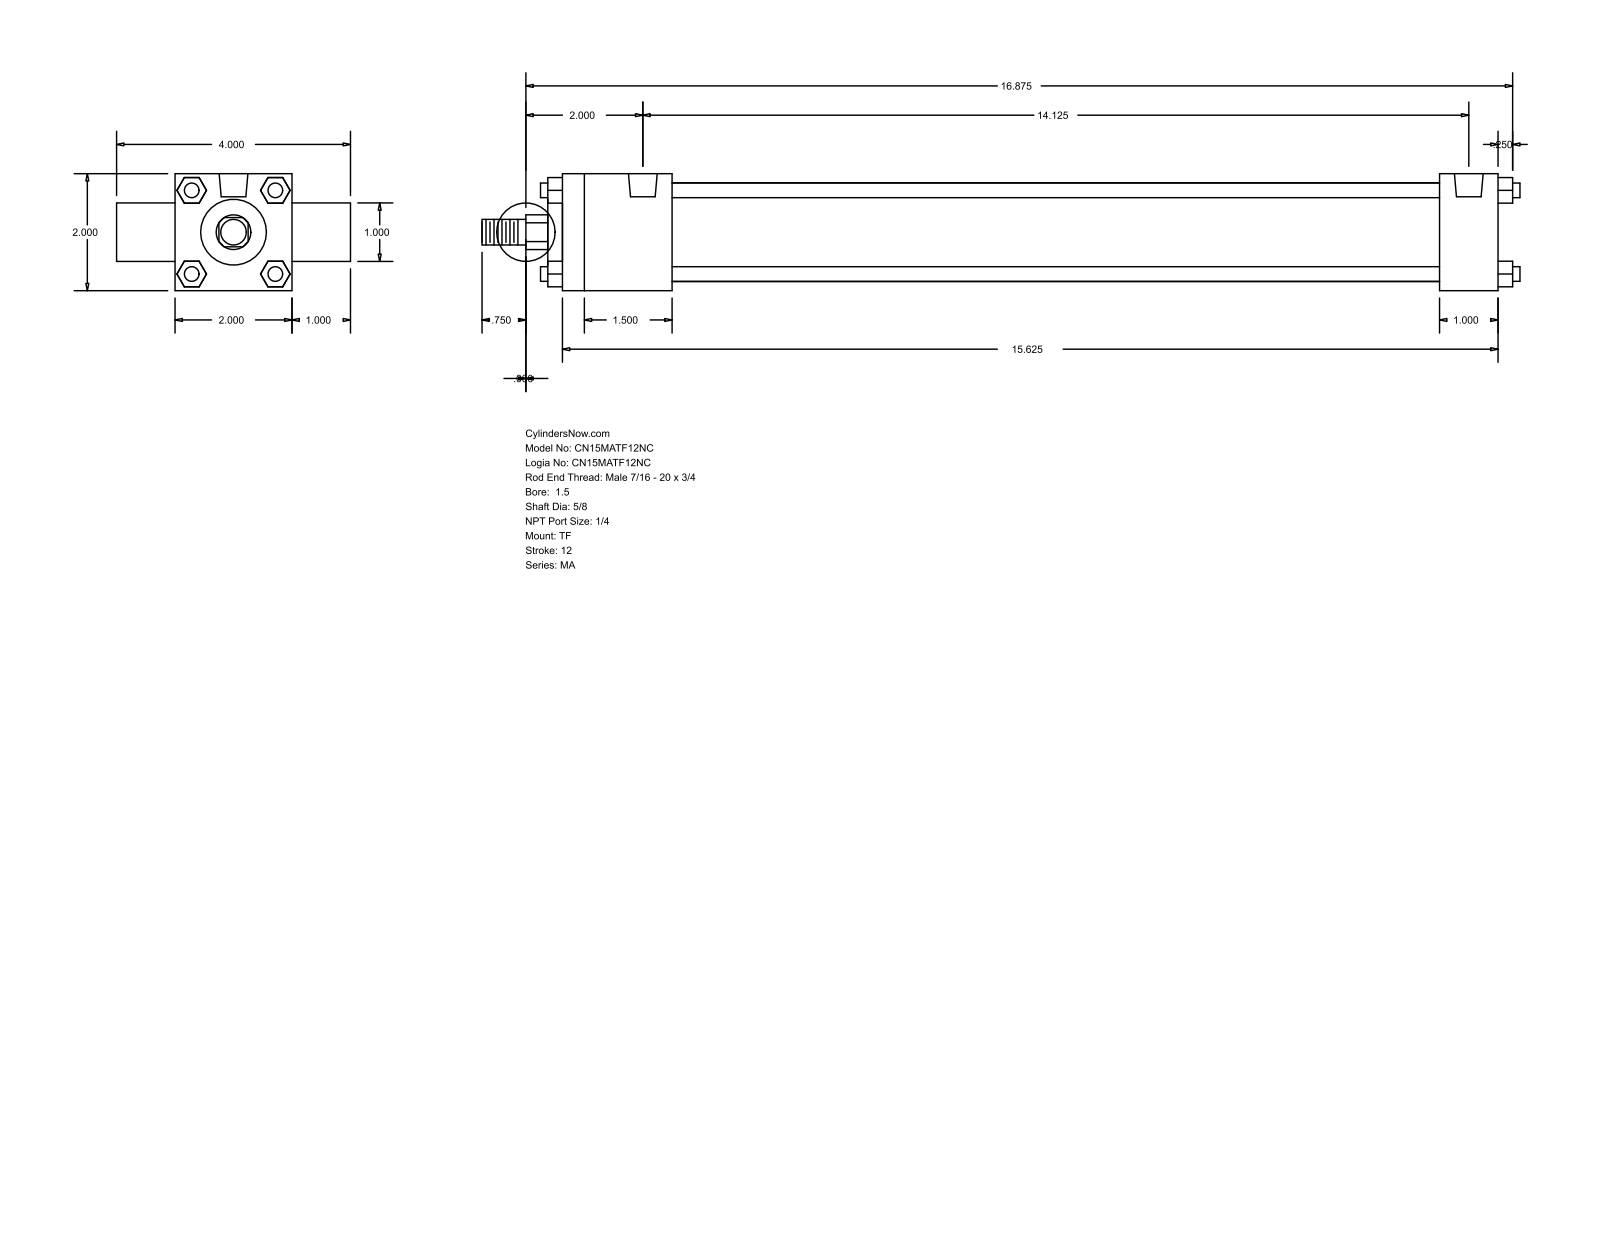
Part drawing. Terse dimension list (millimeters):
name: MA_TF__0150_0.625
written by: GSSL Pune (CONFIG_CONTROL_DESIGN)
unit: mm
bodies: 0 solids, 120 faces (92 planar, 28 cylindrical, 0 other)
size: 450.85 × 101.6 × 50.8
holes: 3× ⌀7.94, 2× ⌀12.49
bosses: 4× ⌀6.35, 1× ⌀42.93, 1× ⌀28.57, 1× ⌀25.4, 1× ⌀15.88, 1× ⌀11.11
rounds: 1× R7.54
face distances: 50.8, 406.39, 25.4, 6.35, 412.74, 76.2, 47.62, 381, 333.38, 358.77
hole spacings: 358.77
